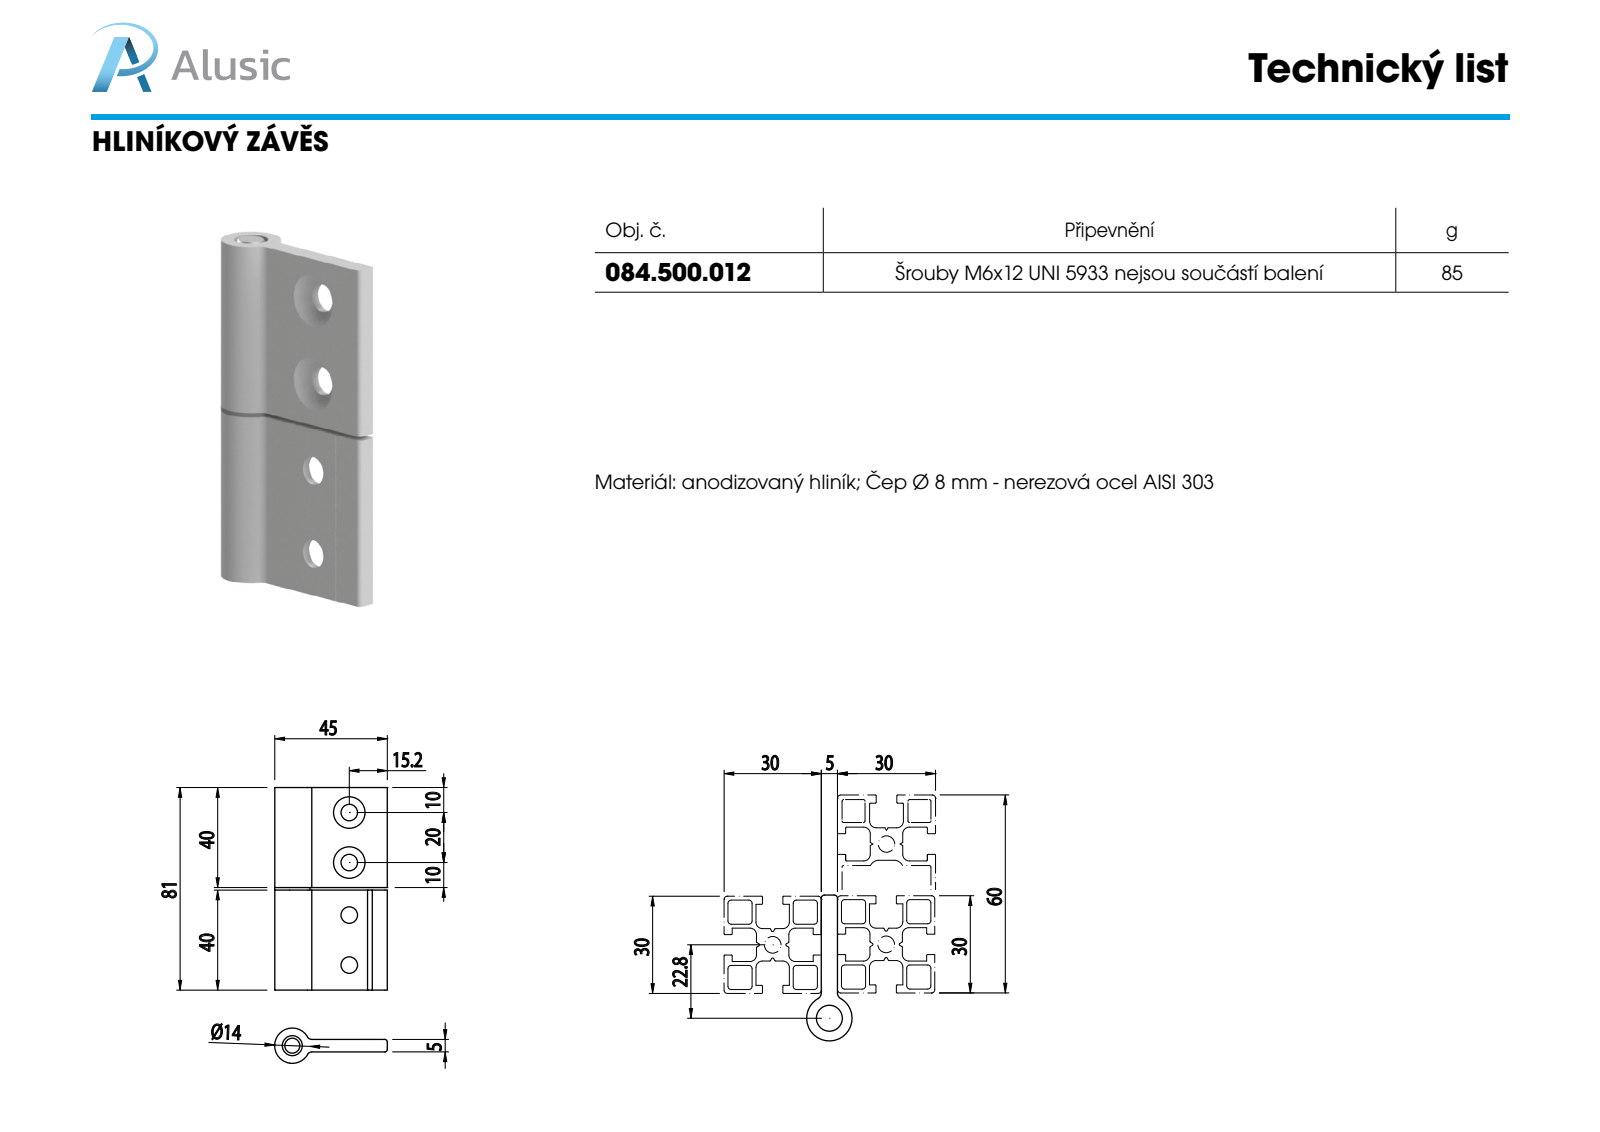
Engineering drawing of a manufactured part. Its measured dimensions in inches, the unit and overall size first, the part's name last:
Units: inches
Overall size (bounding box): 3.189 × 1.774 × 0.555
Round holes (diameter × count): ⌀0.26 ×4, ⌀0.315 ×1, ⌀0.319 ×1
Round bosses / shafts (diameter × count): ⌀0.555 ×1, ⌀0.551 ×1
Partial cylindrical surfaces — rounded edges, fillets, slot ends (radius × count): R0.008 ×2, R0.039 ×2, R0.079 ×2
Main face-to-face distances: 0.197, 1.575, 1.614, 0.039, 3.189, 0.241, 0.241, 0.128, 1.358, 0.217
Hole centre spacings: 0.787, 1.614, 0.827, 2.402
Volume: 1.448 in³ · Surface area: 21.66 in²
Bodies: 4 solids, 188 faces (142 planar, 34 cylindrical, 12 other)
Part name (STEP PRODUCT): 084.500.012; 084.500.001.C; PERNO CERNIERA_084.500.001.B; 084.500.012L
STEP written by: SolidWorks 2011 (CONFIG_CONTROL_DESIGN)
